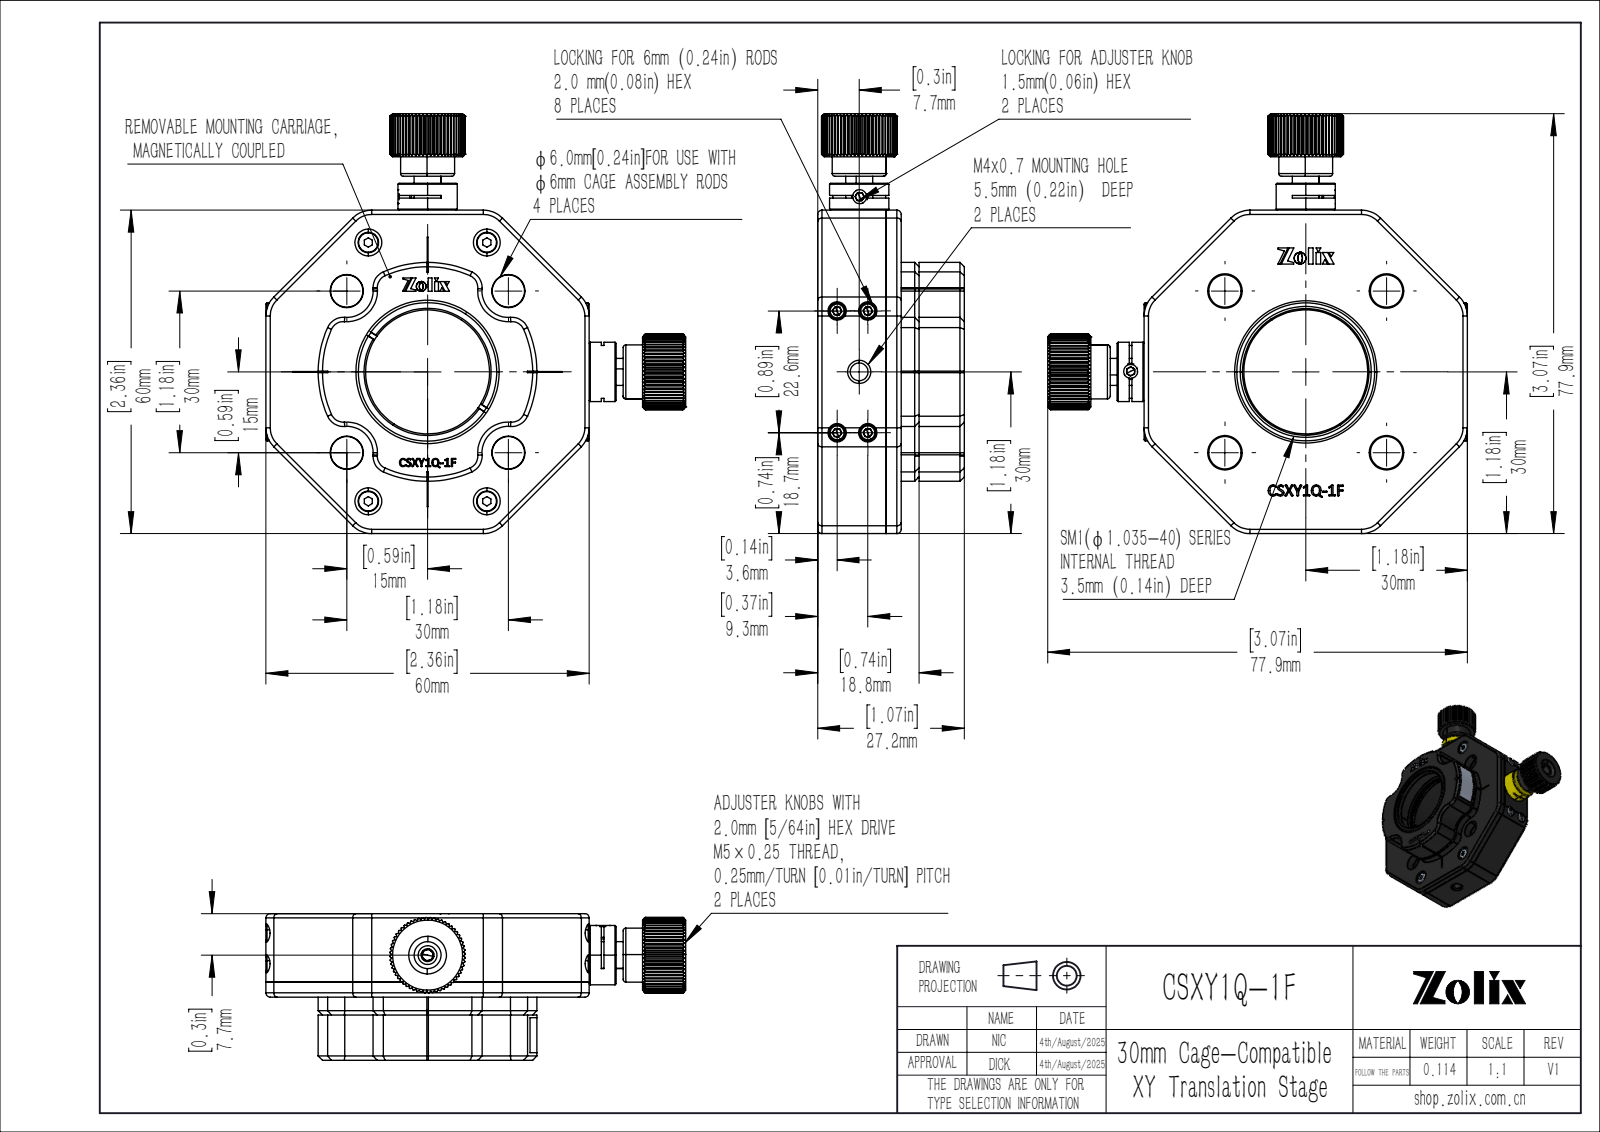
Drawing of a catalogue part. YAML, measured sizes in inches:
part_name: "CSXY1Q-1F"
step_written_by: "SolidWorks 2020 (CONFIG_CONTROL_DESIGN)"
units: inches
bodies: {solids: 44, faces: 2283, planar: 1155, cylindrical: 508, other: 620}
overall_size: [3.067, 3.067, 1.071]
volume: 2.585
surface_area: 49.01
round_holes:
  - {diameter: 0.098, count: 10}
  - {diameter: 0.118, count: 6}
  - {diameter: 0.063, count: 4}
  - {diameter: 0.079, count: 4}
  - {diameter: 0.134, count: 4}
  - {diameter: 0.236, count: 4}
  - {diameter: 0.242, count: 4}
  - {diameter: 0.156, count: 3}
  - {diameter: 0.125, count: 2}
  - {diameter: 0.13, count: 2}
  - {diameter: 0.138, count: 2}
  - {diameter: 0.165, count: 2}
round_bosses_or_shafts:
  - {diameter: 0.118, count: 6}
  - {diameter: 0.059, count: 6}
  - {diameter: 0.15, count: 4}
  - {diameter: 0.079, count: 4}
  - {diameter: 0.433, count: 2}
  - {diameter: 0.394, count: 2}
  - {diameter: 0.299, count: 2}
  - {diameter: 0.197, count: 2}
partial_cylinders:
  - {radius: 0.031, count: 16}
  - {radius: 0.03, count: 12}
  - {radius: 0.126, count: 8}
  - {radius: 0.197, count: 8}
  - {radius: 0.02, count: 4}
  - {radius: 0.079, count: 4}
  - {radius: 0.193, count: 4}
  - {radius: 0.039, count: 2}
face_to_face_distances: [0.11, 0.5, 0.61, 0.13, 2.362, 0.74, 0.24, 0.14, 0.36, 0.47]
hole_center_spacings: [0.176, 0.388, 0.646, 0.657, 0.835, 1.039, 1.083, 1.181]
